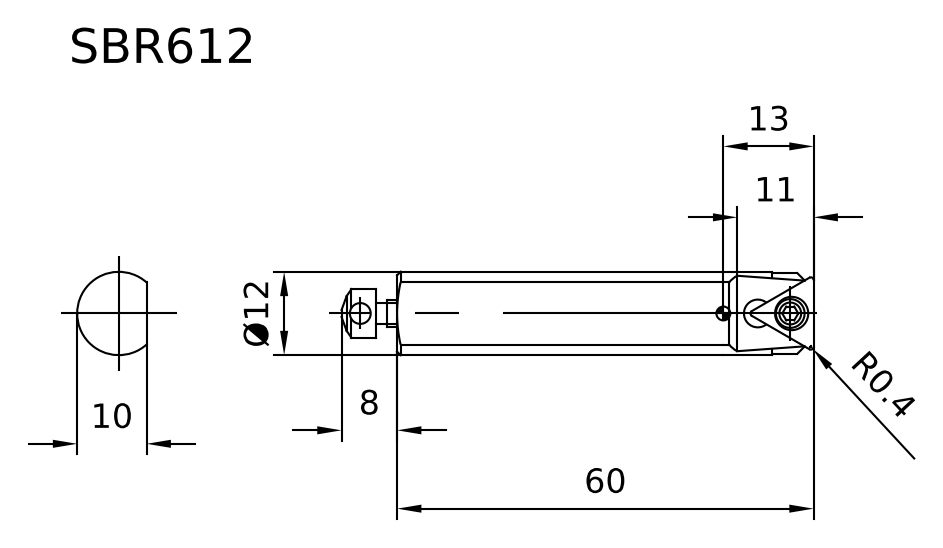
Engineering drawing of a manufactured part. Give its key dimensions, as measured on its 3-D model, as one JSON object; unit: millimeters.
{"part_name": "SBR612_ASM", "step_written_by": "SIEMENS PLM Software NX 10.0 (AUTOMOTIVE_DESIGN)", "units": "millimeters", "bodies": {"solids": 3, "faces": 93, "planar": 23, "cylindrical": 42, "other": 28}, "overall_size": [66.56, 12, 10.36], "volume_mm3": 5770, "surface_area_mm2": 3018, "round_holes": [[1.8, 2], [3, 1], [3.3, 1]], "round_bosses_or_shafts": [[7, 1], [4.1, 1], [4, 1], [3, 1]], "partial_cylinders_radius": [[0.22, 6], [0.47, 6], [0.1, 4], [0.5, 1], [1.5, 1], [5.8, 1], [6, 1]], "face_to_face_distances": [2.88, 2, 3, 3.68, 0.8, 54.06, 56.06, 7, 47.06, 9]}
